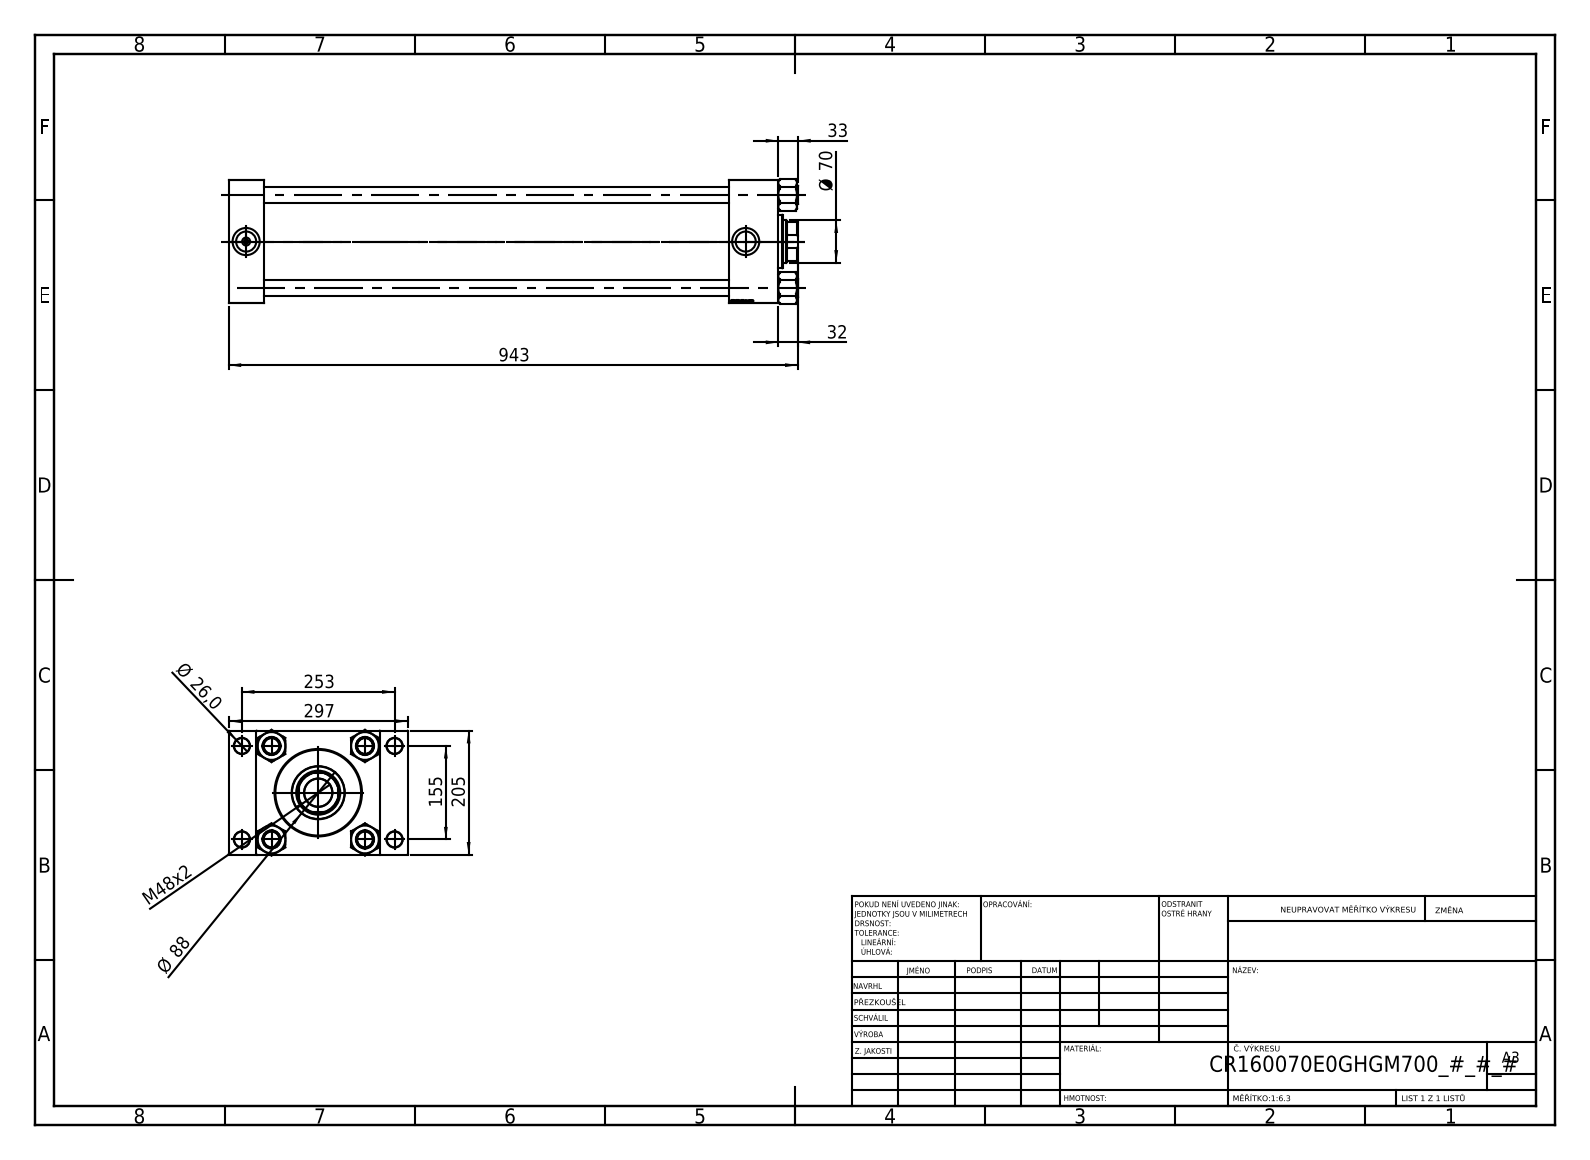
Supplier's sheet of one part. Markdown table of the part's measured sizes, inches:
| quantity | value |
| --- | --- |
| part name | V215CR_E_Body; V215CR_TYCINKA_E; V215_VC_A; NUT_M5_E (+1 more) |
| STEP written by | SolidWorks 2019 (CONFIG_CONTROL_DESIGN) |
| units | inches |
| bodies | 11 solids, 1184 faces (546 planar, 86 cylindrical, 552 other) |
| overall size | 37.165 × 11.693 × 8.194 |
| volume | 832.4 in³ |
| surface area | 2 878 in² |
| round holes (diameter × count) | 1.024 × 4, 1.063 × 4, 0.276 × 2, 1.309 × 2, 1.772 × 2, 1.831 × 1, 2.756 × 1, 2.874 × 1, 4.724 × 1, 5.591 × 1, 6.299 × 1 |
| round bosses / shafts (diameter × count) | 1.181 × 4, 6.535 × 1, 3.465 × 1 |
| partial cylindrical surfaces (radius × count) | 1.339 × 1 |
| main face-to-face distances | 2.283, 8.071, 35.866, 33.583, 32.677, 30.394, 3.189, 1.811, 9.882, 34.736 |
| hole center spacings | 1.931, 4.312, 5.841, 6.098, 6.399, 8.03, 10.084, 6.102 |
